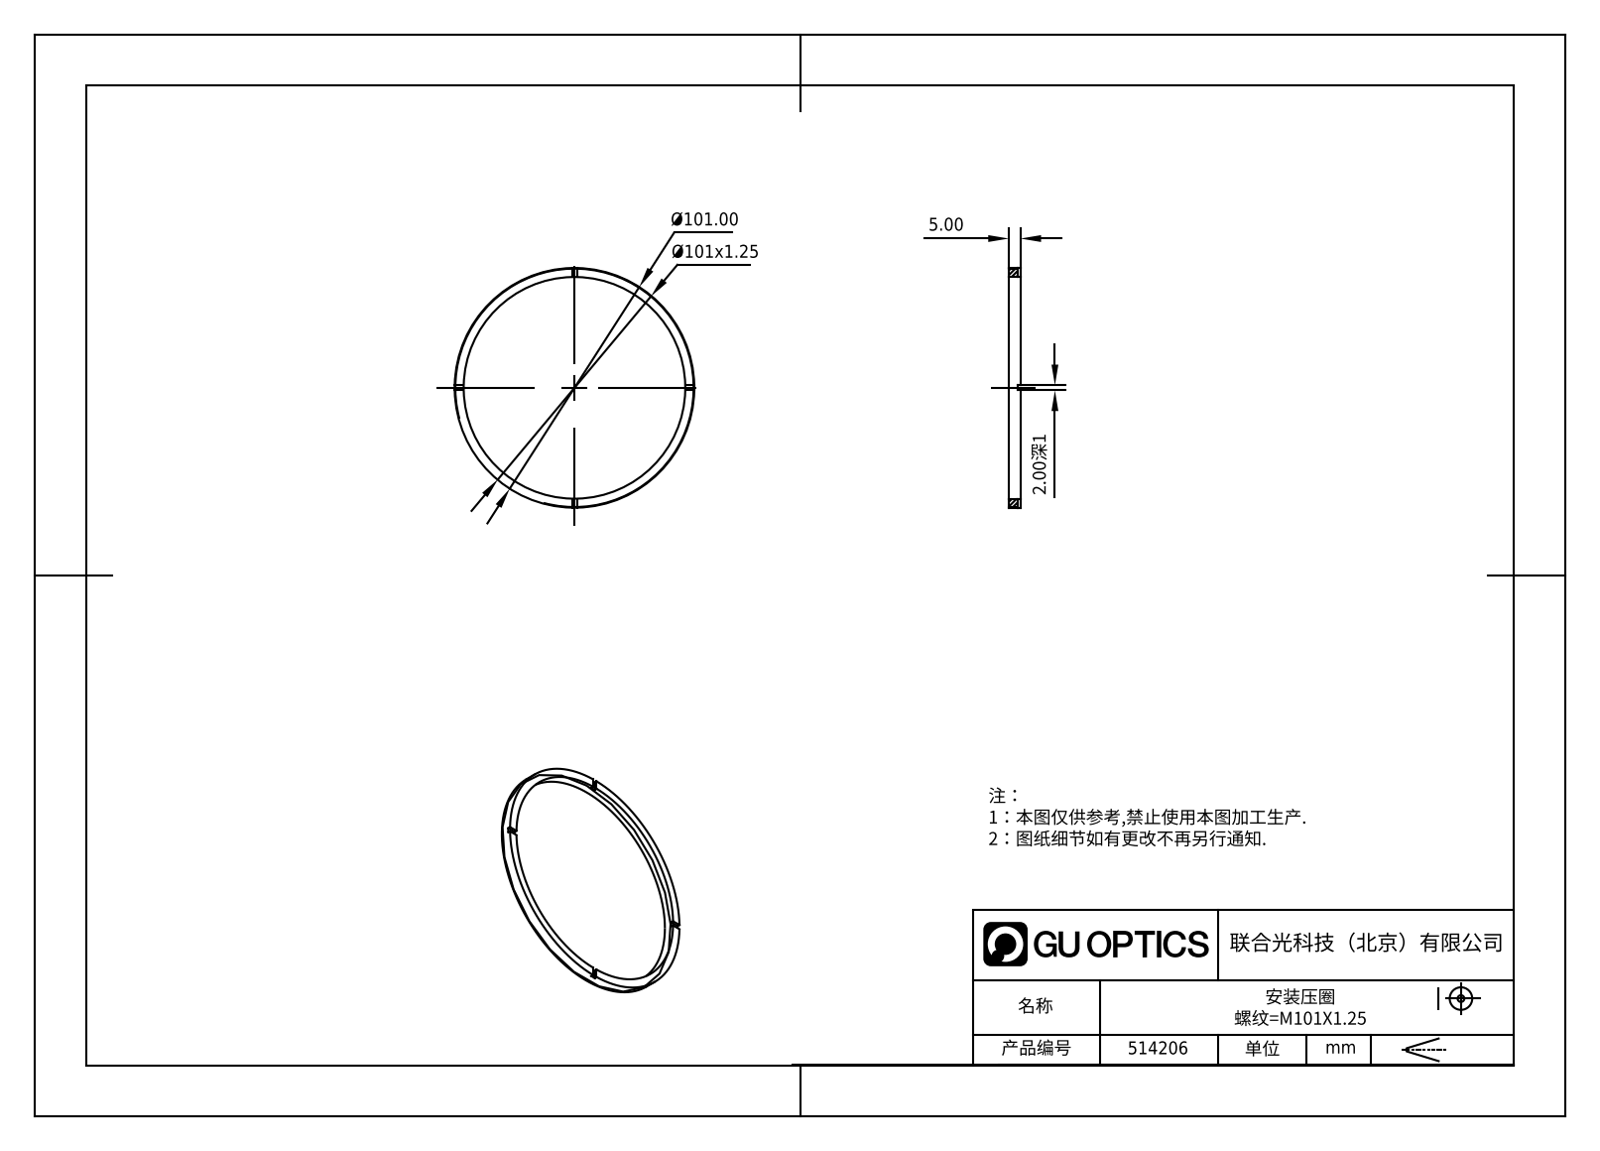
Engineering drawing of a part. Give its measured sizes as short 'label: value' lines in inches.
name: 514206
written by: SolidWorks 2020 (CONFIG_CONTROL_DESIGN)
unit: in
bodies: 1 solid, 21 faces (17 planar, 4 cylindrical, 0 other)
size: 3.976 × 3.976 × 0.197
volume: 0.37 in³; area: 8.527 in²
holes: 1× ⌀3.661
bosses: 1× ⌀3.976
face distances: 0.197, 0.157, 0.039, 0.079
